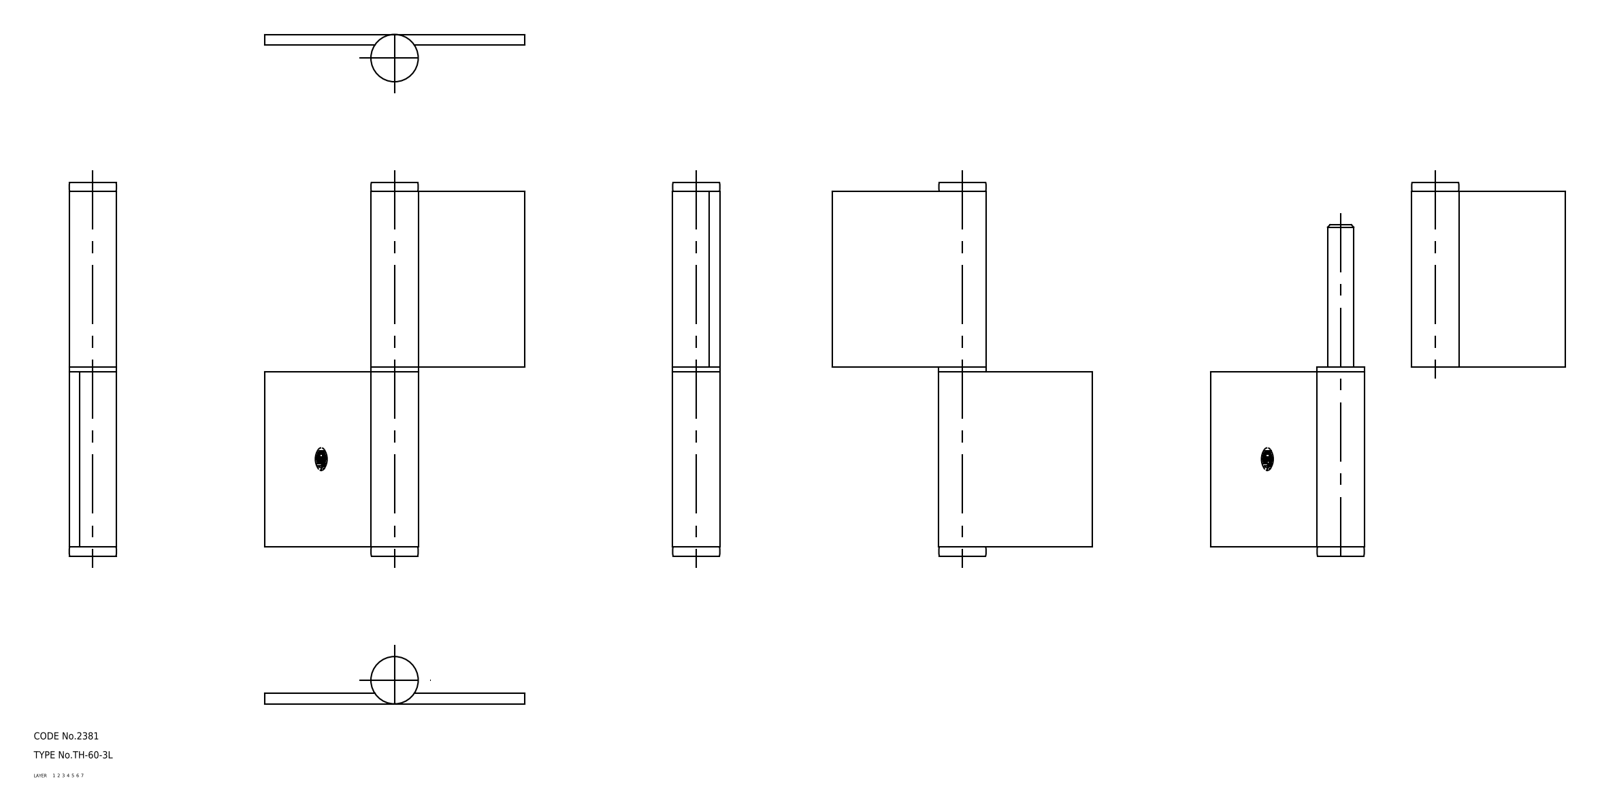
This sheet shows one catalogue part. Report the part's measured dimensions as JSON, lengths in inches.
{"part_name": "hinge piece; washer; shaft; rivet (+1 more)", "step_written_by": "CADfix (AUTOMOTIVE_DESIGN)", "units": "inches", "bodies": {"solids": 5, "faces": 34, "planar": 0, "cylindrical": 0, "other": 34}, "overall_size": [6.22, 4.331, 0.787], "volume_in3": 4.927, "surface_area_in2": 60.23}
